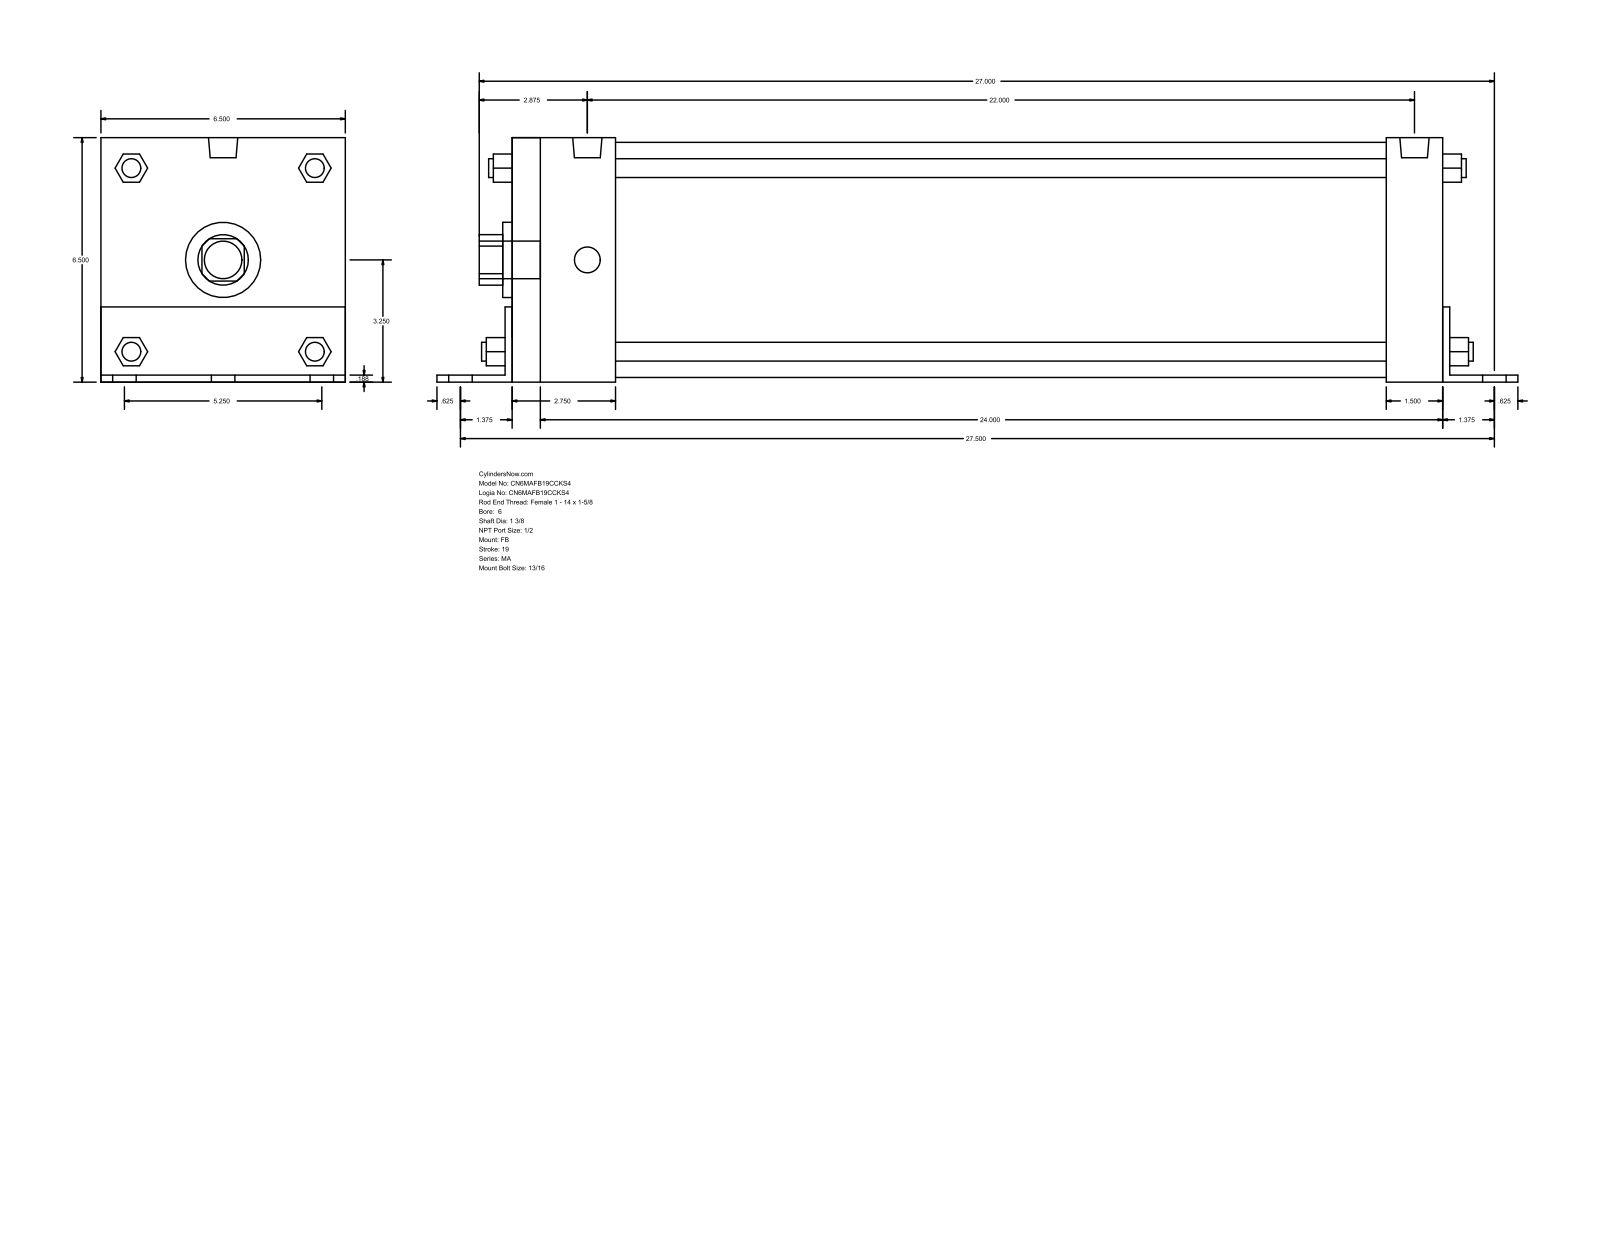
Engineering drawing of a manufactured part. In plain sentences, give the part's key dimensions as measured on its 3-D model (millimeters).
The part is named "MA_FB__0600_1.375". Its 3-D file was written by "GSSL Pune (CONFIG_CONTROL_DESIGN)". It is 0 solids with 140 faces: 105 planar, 35 cylindrical and 0 other. Overall it measures 727.08 by 165.15 by 165.1 millimeters. Round holes: 1 of diameter 34.92, 1 of diameter 50.8, 1 of diameter 158.75. Round bosses or shafts: 6 of diameter 20.64, 4 of diameter 17.46, 4 of diameter 12.7, 2 of diameter 19.77, 1 of diameter 25.4. Partial cylindrical surfaces (rounded edges, fillets, slot ends): 1 of radius 17.06, 1 of radius 32.05. The main face-to-face distances are 165.1, 4.76, 625.47, 165.15, 4.71, 160.39, 4.77, 38.1, 630.24, 635.
